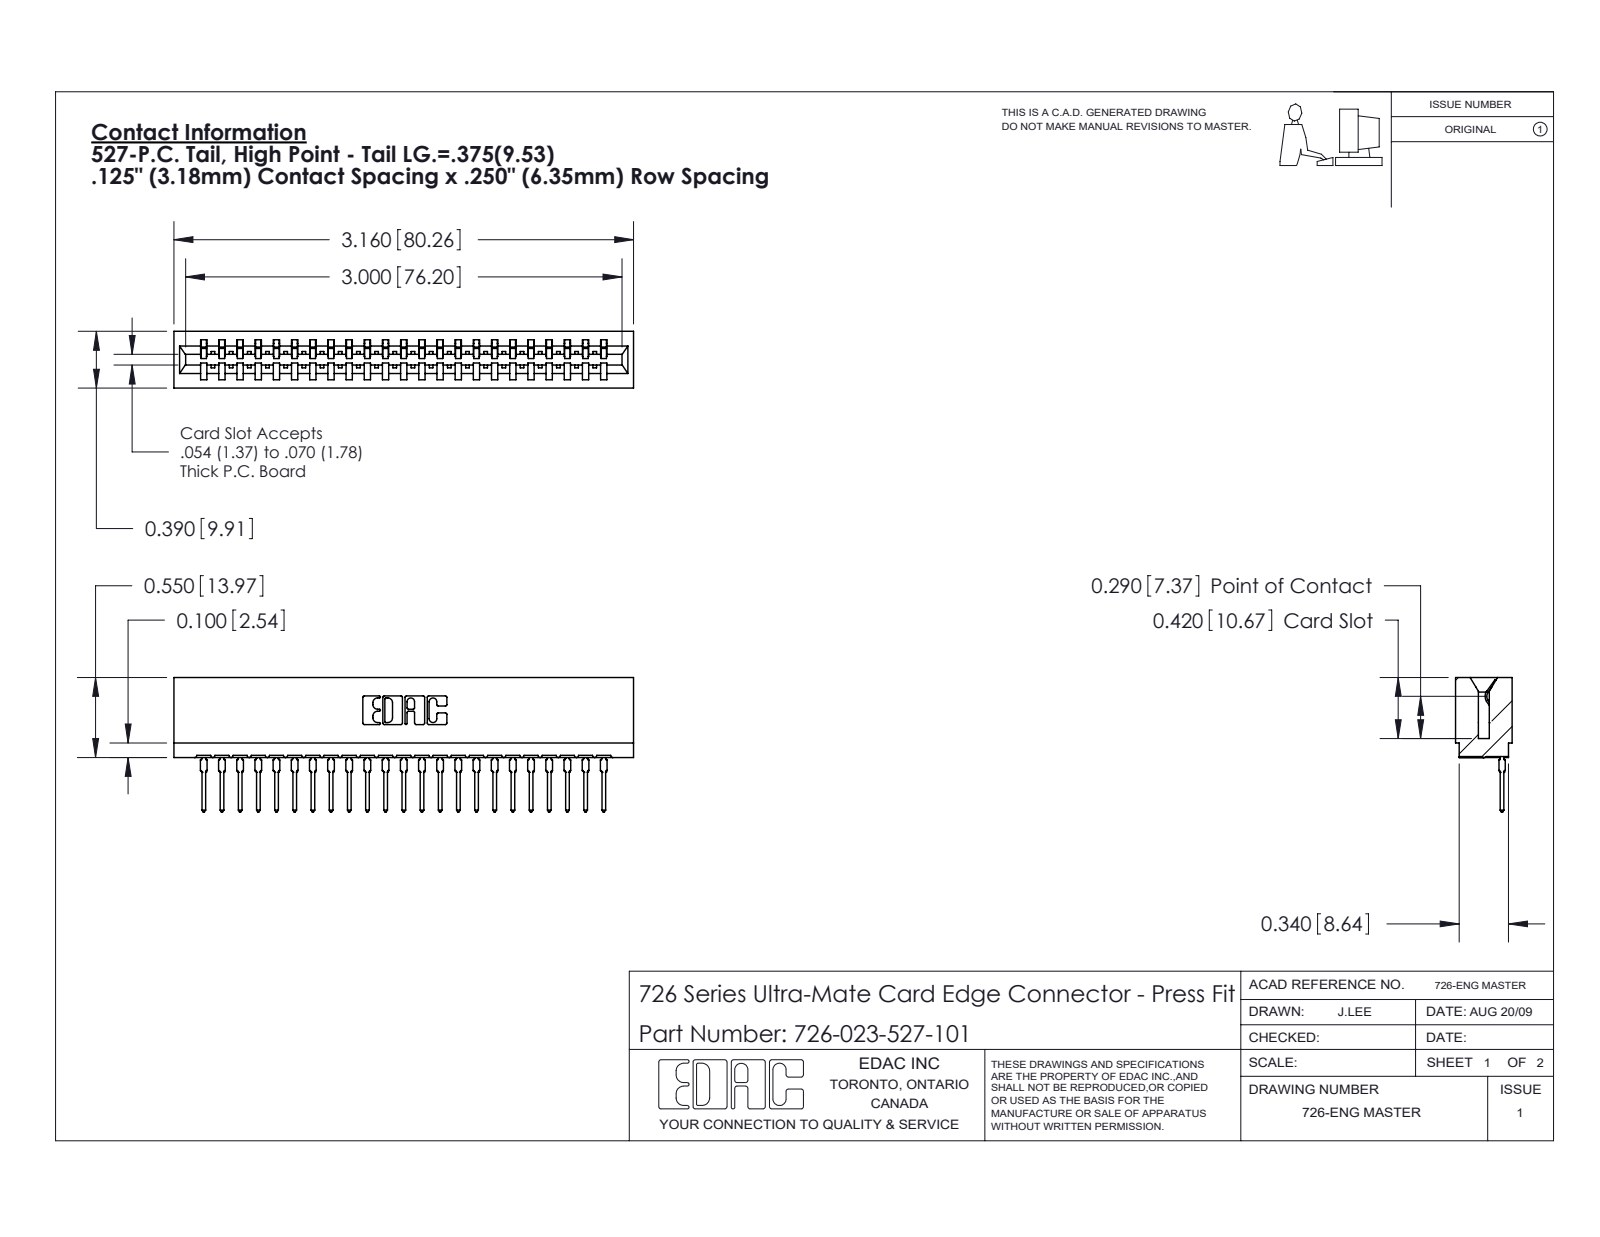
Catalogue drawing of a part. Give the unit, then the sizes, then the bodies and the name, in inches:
Units: inches
Overall size (bounding box): 3.16 × 0.924 × 0.39
Partial cylindrical surfaces — rounded edges, fillets, slot ends (radius × count): R0.021 ×46, R0.015 ×24, R0.01 ×22, R0.007 ×6, R0.031 ×6, R0.005 ×4, R0.011 ×4, R0.026 ×3
Main face-to-face distances: 0.057, 0.333, 0.39, 0.025, 0.307, 0.75, 0.25, 0.042, 0.5, 0.125
Volume: 0.445 in³ · Surface area: 17.03 in²
Bodies: 24 solids, 2581 faces (1504 planar, 479 cylindrical, 598 other)
Part name (STEP PRODUCT): 746-292-001_527; 726 Part_.515 Slot Depth - 01; 726-023-527-101
STEP written by: SolidWorks 2020 (CONFIG_CONTROL_DESIGN)
